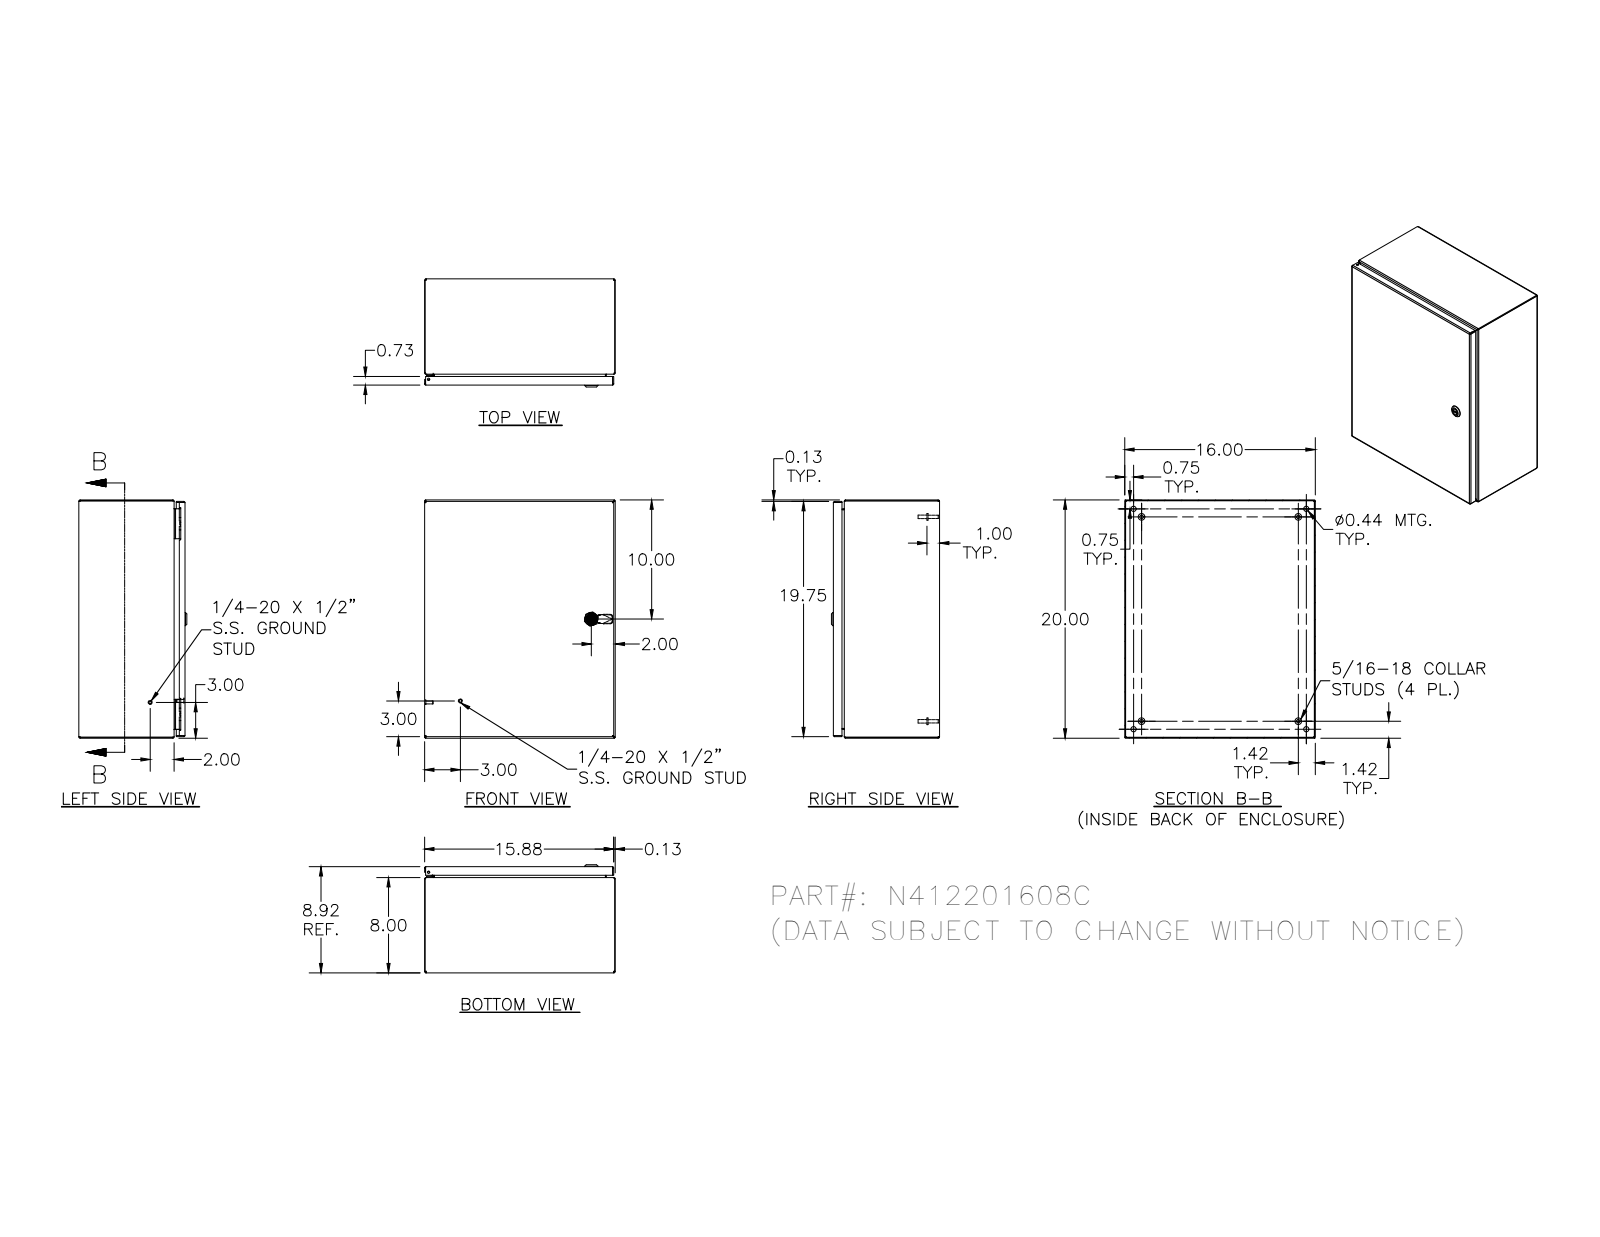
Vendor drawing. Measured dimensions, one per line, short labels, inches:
name: N412201608C
written by: SolidWorks 2018 (AUTOMOTIVE_DESIGN)
unit: in
bodies: 33 solids, 1449 faces (530 planar, 547 cylindrical, 372 other)
size: 20 × 16 × 9.075
volume: 101 in³; area: 2 747 in²
holes: 5× ⌀0.188, 4× ⌀0.093, 4× ⌀0.152, 4× ⌀0.167, 4× ⌀0.172, 4× ⌀0.437, 2× ⌀0.156, 1× ⌀0.187, 1× ⌀0.197, 1× ⌀0.315, 1× ⌀0.394, 1× ⌀0.402
bosses: 10× ⌀0.25, 5× ⌀0.131, 4× ⌀0.563, 4× ⌀0.36, 4× ⌀0.32, 4× ⌀0.3, 4× ⌀0.275, 4× ⌀0.256
rounds: 30× R0.012, 30× R0.031, 26× R0.05, 20× R0.105, 18× R0.016, 16× R0.125, 13× R0.02, 8× R0.032
face distances: 0.074, 8.843, 8.769, 8.917, 0.074, 15.926, 16, 15.852, 15.926, 19.852
hole spacings: 16, 0.66, 0.656, 1.307, 1.965, 15.34, 16.66, 15.614
